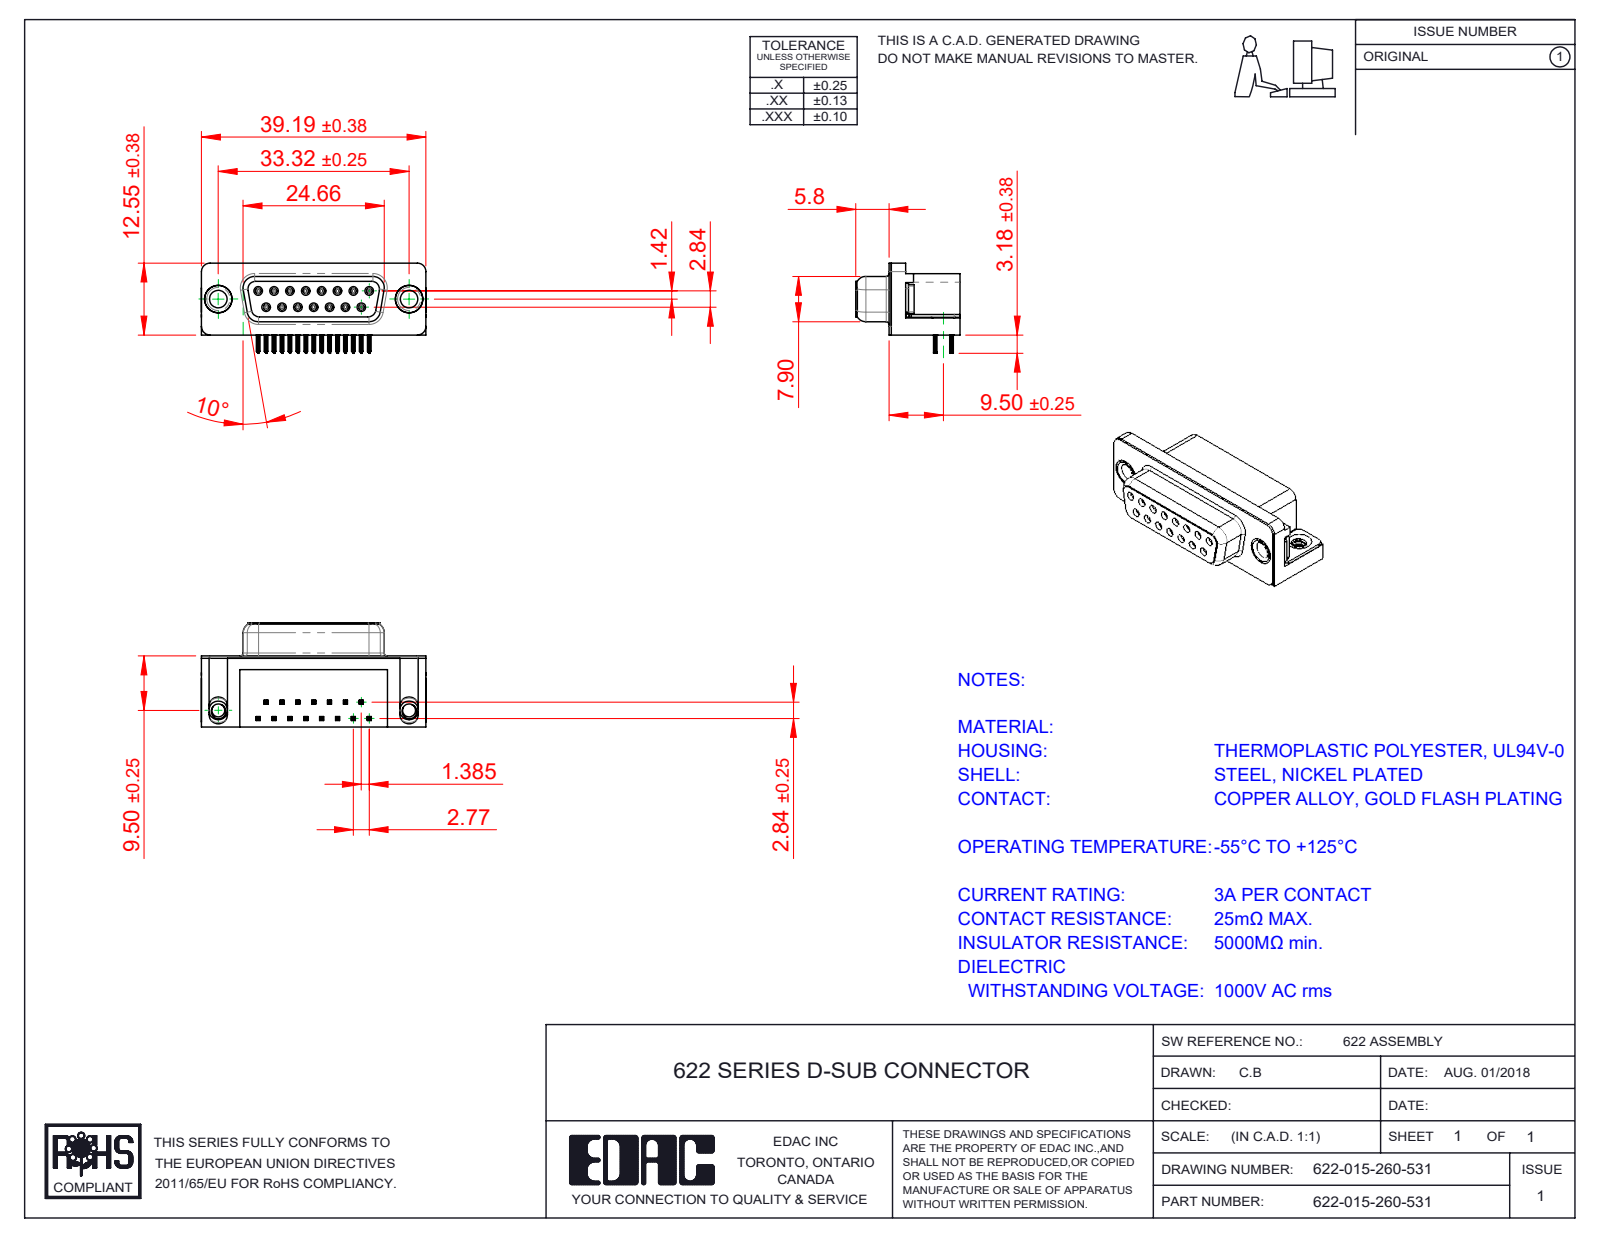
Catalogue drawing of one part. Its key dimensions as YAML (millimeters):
part_name: "622 Thru Hole Rivet; 622 Housing_15 Socket; 622 Shell_15 Socket; 622 2 Prong Board Lock (+3 more)"
step_written_by: "SolidWorks 2016 (CONFIG_CONTROL_DESIGN)"
units: millimeters
bodies: {solids: 21, faces: 2427, planar: 1106, cylindrical: 595, other: 726}
overall_size: [39.22, 18.2, 16.25]
volume: 5175
surface_area: 6698
round_holes:
  - {diameter: 0.8, count: 15}
  - {diameter: 0.9, count: 15}
  - {diameter: 3.05, count: 2}
  - {diameter: 4, count: 2}
  - {diameter: 4.8, count: 2}
  - {diameter: 5, count: 2}
round_bosses_or_shafts:
  - {diameter: 1.2, count: 15}
  - {diameter: 4.9, count: 2}
  - {diameter: 4.75, count: 2}
  - {diameter: 3.85, count: 2}
partial_cylinders:
  - {radius: 0.1, count: 120}
  - {radius: 0.15, count: 60}
  - {radius: 0.35, count: 30}
  - {radius: 1, count: 18}
  - {radius: 0.34, count: 15}
  - {radius: 0.5, count: 10}
  - {radius: 0.25, count: 8}
  - {radius: 1.35, count: 8}
face_to_face_distances: [0.4, 12, 6.2, 12.4, 10.35, 2.9, 0.85, 6.65, 0.35, 0.5]
hole_center_spacings: [3.16, 2.77, 5.54, 8.31, 11.08, 5.03, 5.04, 7.48]
